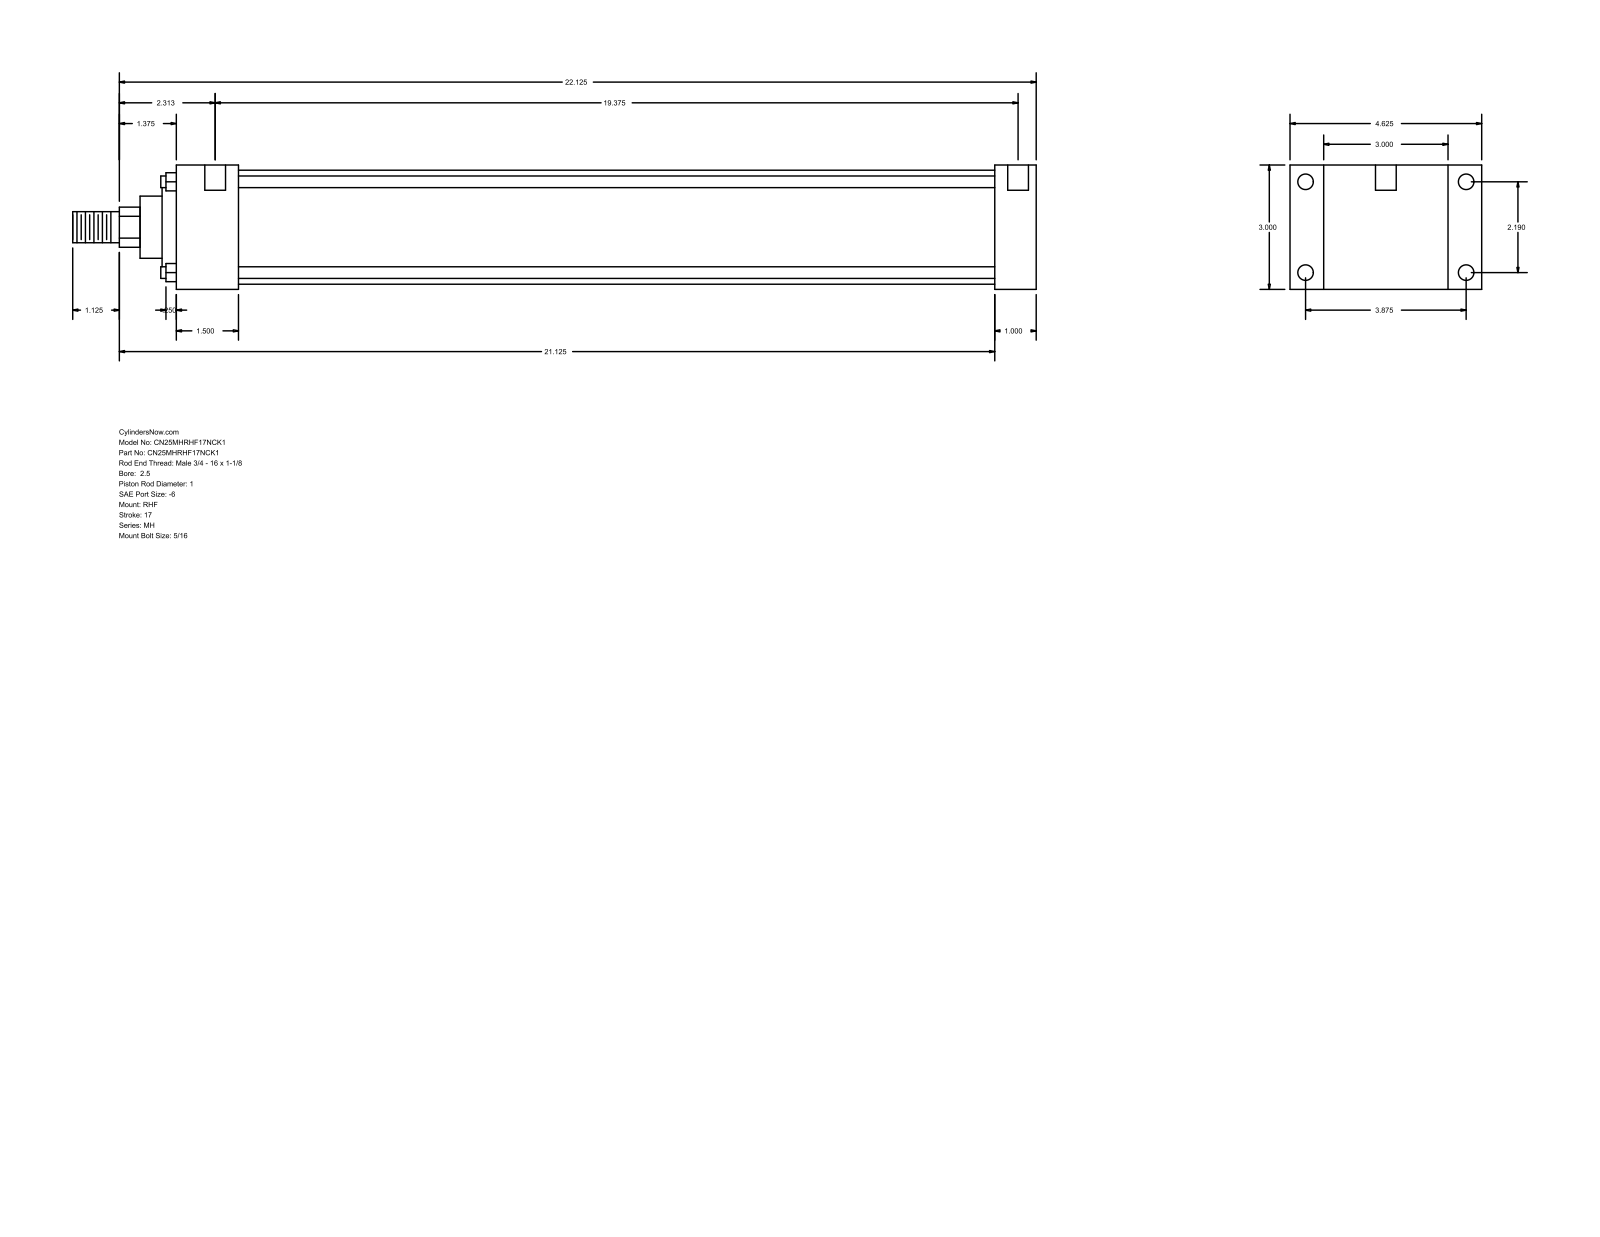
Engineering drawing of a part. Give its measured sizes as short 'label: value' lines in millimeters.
name: MH_RHF__0250_1
written by: GSSL Pune (CONFIG_CONTROL_DESIGN)
unit: mm
bodies: 0 solids, 90 faces (61 planar, 29 cylindrical, 0 other)
size: 590.55 × 117.47 × 76.2
holes: 4× ⌀5.56, 4× ⌀9.53, 2× ⌀12.7
bosses: 4× ⌀7.14, 1× ⌀69.85, 1× ⌀60.33, 1× ⌀38.1, 1× ⌀25.4, 1× ⌀19.05
rounds: 1× R12.29
face distances: 76.2, 25.4, 20.64, 96.84, 501.66, 527.06, 117.48, 38.11, 463.55, 488.95
hole spacings: 55.62, 98.42, 113.05, 500.06, 3.18, 4.76, 492.12, 495.3
